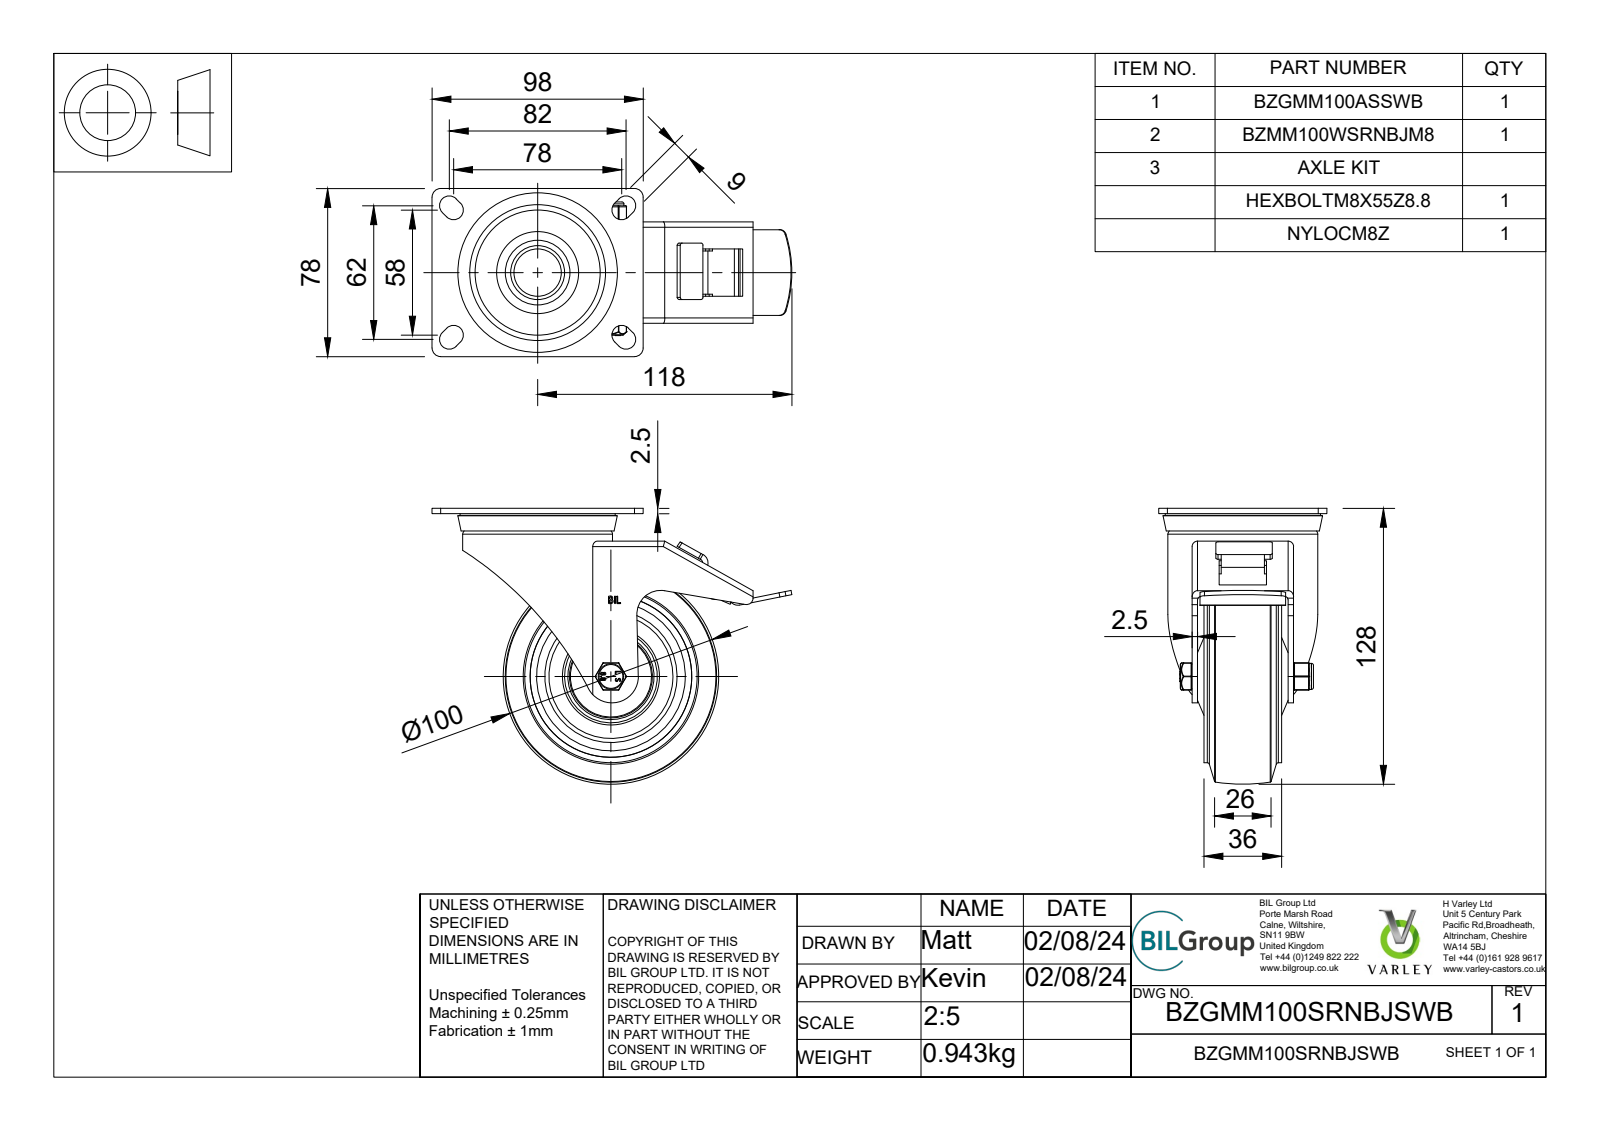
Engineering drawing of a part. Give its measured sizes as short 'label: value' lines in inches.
name: BZGMM100SRNBJSWB v3; BZGMM100ASSWB - 2 - 42 v1; ZINC PLATED, PRESSED STEEL FORKS (1); BRAKE PAD (1) (+8 more)
written by: Autodesk Translation Framework v13.14.0.145 (AUTOMOTIVE_DESIGN)
unit: in
bodies: 53 solids, 857 faces (336 planar, 219 cylindrical, 302 other)
size: 6.575 × 5.039 × 3.071
volume: 17.14 in³; area: 231.6 in²
holes: 2× ⌀0.026, 2× ⌀1.024, 2× ⌀1.181, 1× ⌀0.315, 1× ⌀0.323, 1× ⌀0.339, 1× ⌀0.591, 1× ⌀0.787, 1× ⌀0.886, 1× ⌀1.22, 1× ⌀1.26, 1× ⌀1.299
bosses: 1× ⌀3.15, 1× ⌀2.736, 1× ⌀1.85, 1× ⌀1.693, 1× ⌀1.516, 1× ⌀1.378, 1× ⌀1.201, 1× ⌀1.102
rounds: 18× R0.02, 12× R0.01, 8× R0.049, 8× R0.177, 5× R0.157, 4× R0.013, 4× R0.025, 4× R0.039
face distances: 0.098, 0.118, 1.752, 0.217, 1.043, 0.709, 1.654, 0.6, 0.039, 0.079
hole spacings: 0.127, 0.098
